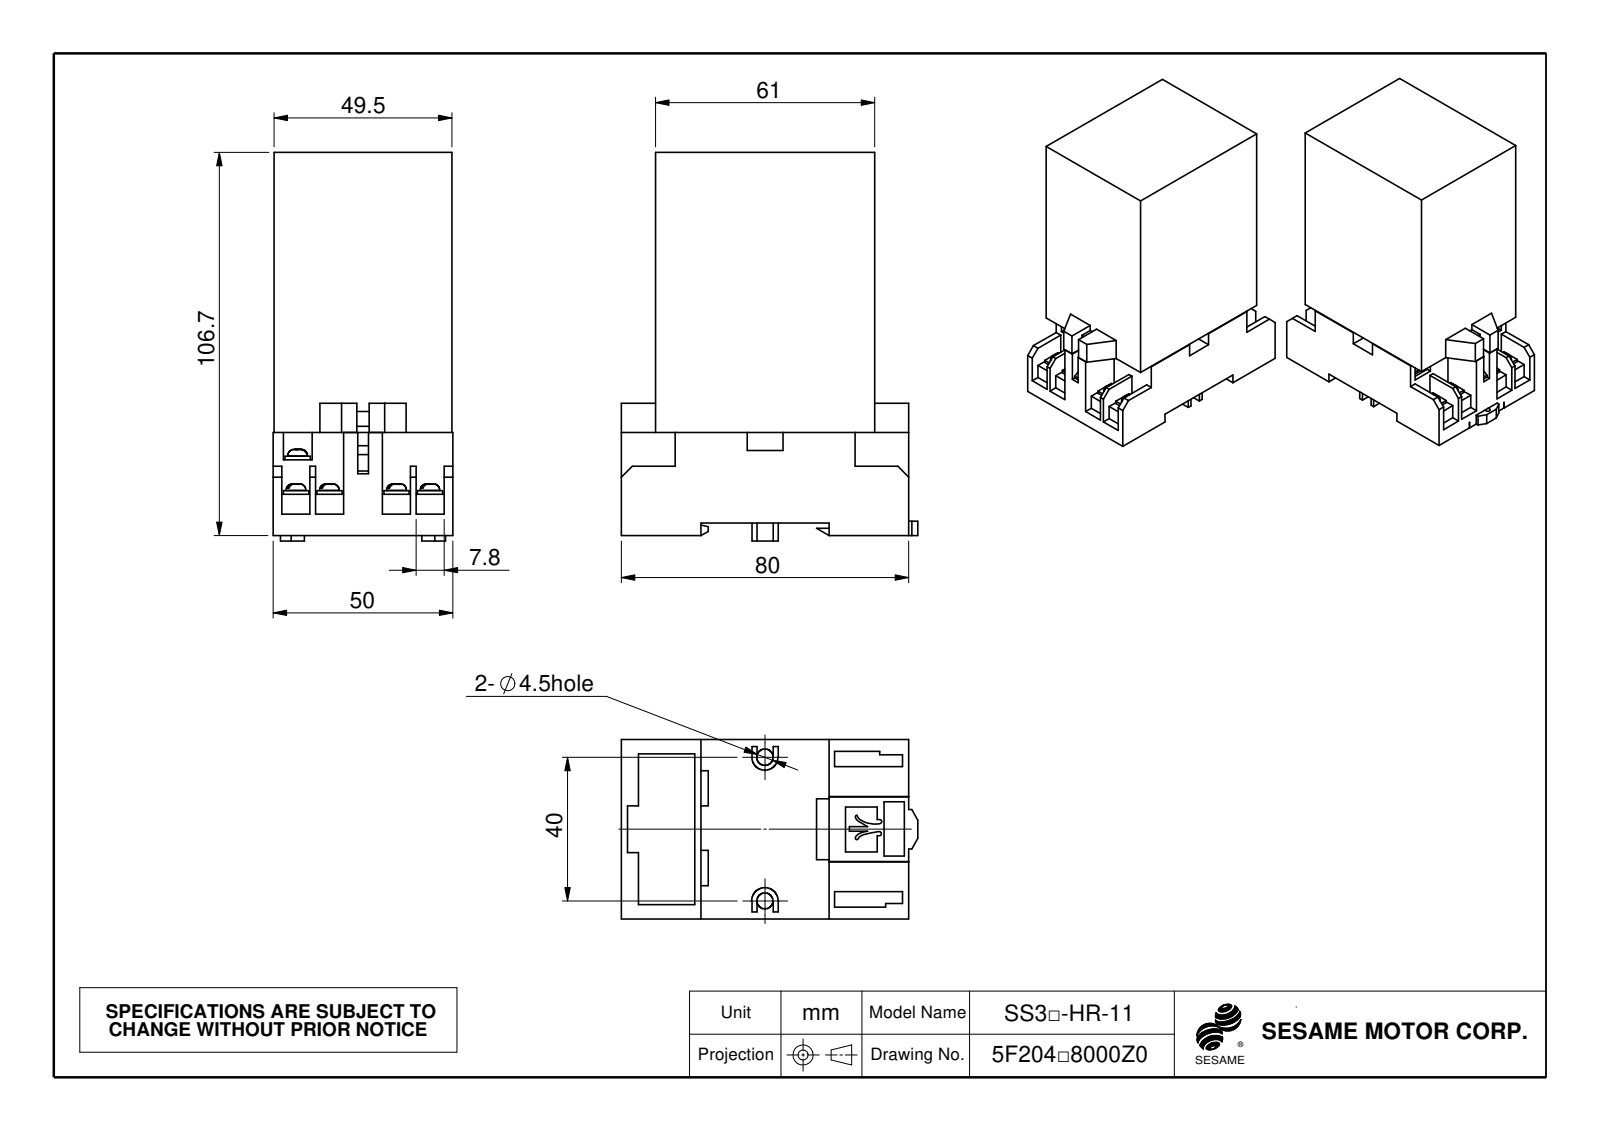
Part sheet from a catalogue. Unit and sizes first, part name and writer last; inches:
Units: inches
Overall size (bounding box): 4.26 × 3.248 × 1.969
Round holes (diameter × count): ⌀0.118 ×11, ⌀0.236 ×7, ⌀0.252 ×4, ⌀0.177 ×2, ⌀0.072 ×1
Round bosses / shafts (diameter × count): ⌀0.217 ×11, ⌀0.079 ×11, ⌀0.315 ×1
Partial cylindrical surfaces — rounded edges, fillets, slot ends (radius × count): R0.012 ×44, R0.02 ×4, R0.144 ×2, R0.039 ×1, R0.531 ×1
Main face-to-face distances: 1.949, 2.402, 1.959, 3.071, 0.118, 1.969, 0.677, 0.374, 0.992, 4.063
Hole centre spacings: 0.366, 1.102, 1.198, 1.268, 1.664, 1.936, 2.394, 2.422
Volume: 19.69 in³ · Surface area: 79.28 in²
Bodies: 24 solids, 803 faces (558 planar, 177 cylindrical, 68 other)
Part name (STEP PRODUCT): 11-PIN_Default
STEP written by: SolidWorks 2010 (CONFIG_CONTROL_DESIGN)
